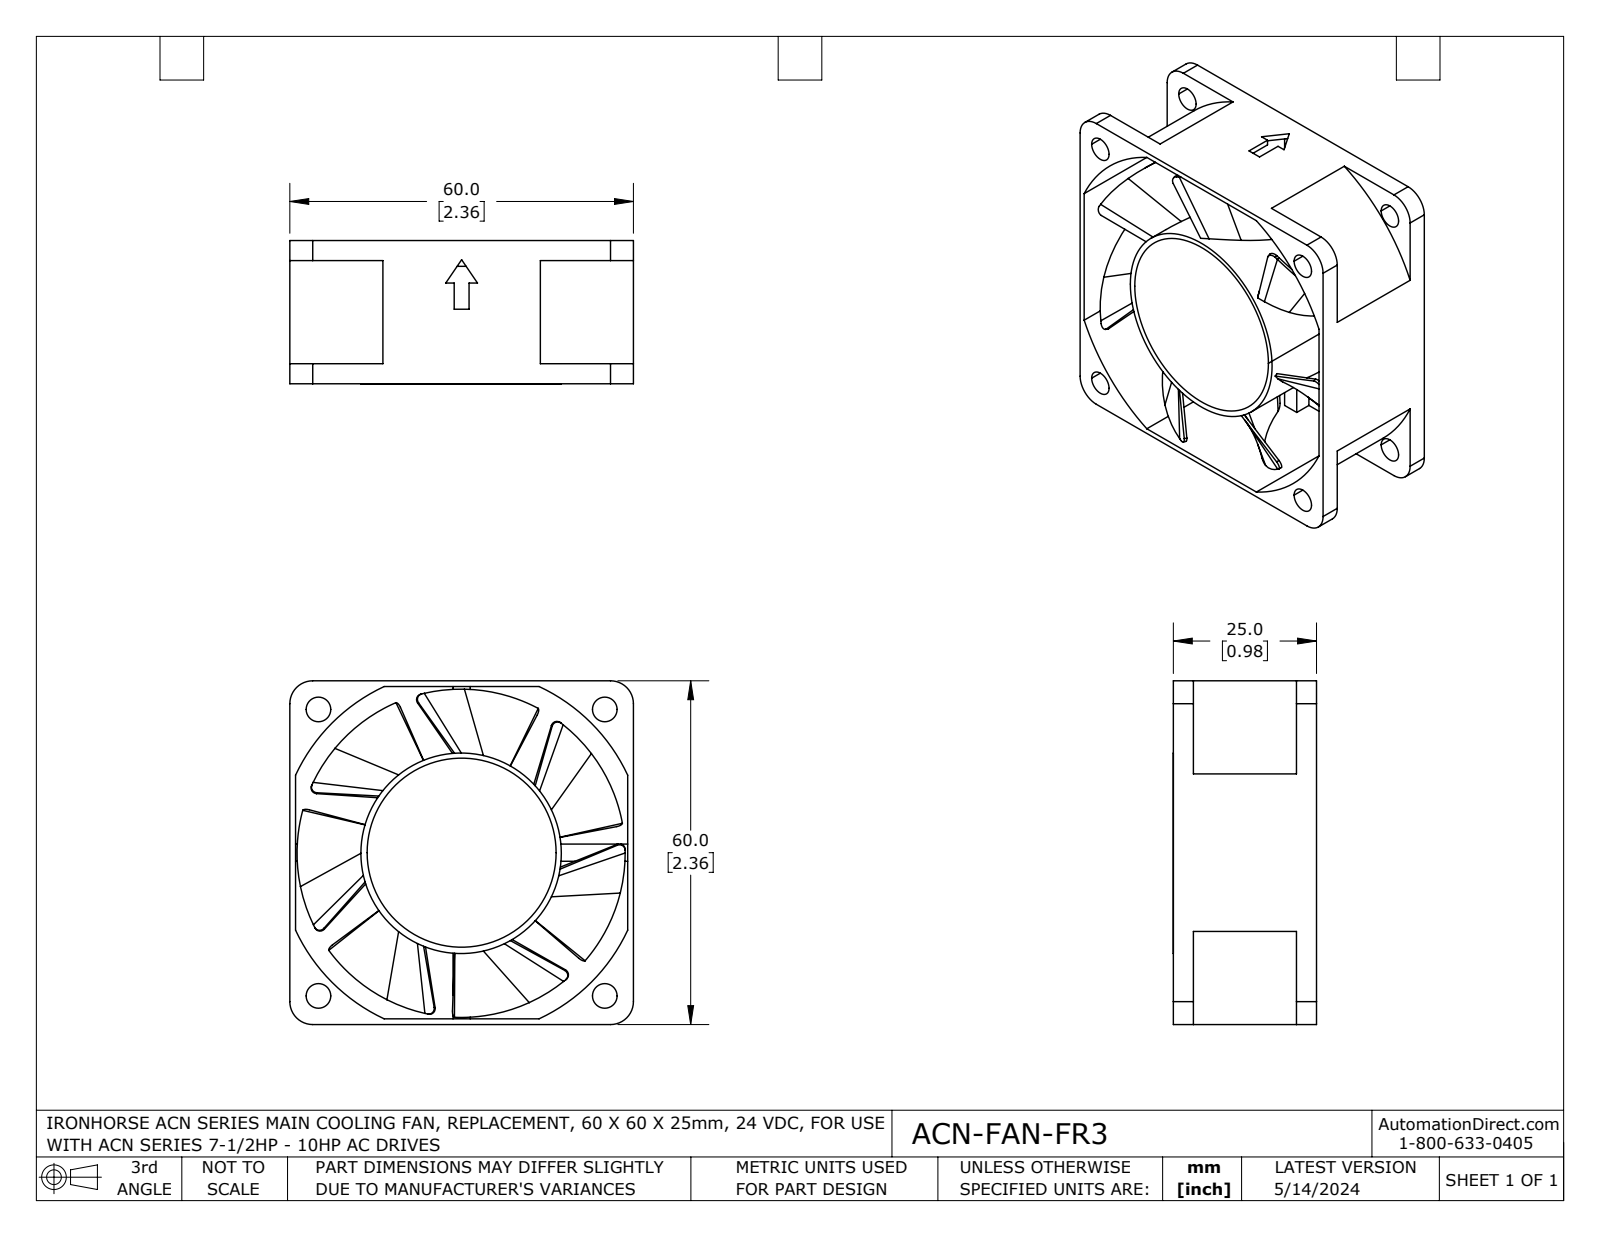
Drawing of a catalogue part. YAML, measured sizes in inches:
part_name: "ACN-FAN-FR3"
step_written_by: "SolidWorks 2021 (AUTOMOTIVE_DESIGN)"
units: inches
bodies: {solids: 2, faces: 187, planar: 42, cylindrical: 40, other: 105}
overall_size: [2.362, 2.362, 0.984]
volume: 2.022
surface_area: 42.74
round_holes:
  - {diameter: 0.169, count: 4}
  - {diameter: 1.161, count: 1}
  - {diameter: 1.299, count: 1}
round_bosses_or_shafts:
  - {diameter: 1.378, count: 1}
  - {diameter: 1.299, count: 1}
partial_cylinders:
  - {radius: 0.157, count: 4}
  - {radius: 1.26, count: 1}
  - {radius: 1.299, count: 1}
face_to_face_distances: [0.039, 2.323, 2.362, 2.283, 0.945, 0.984, 0.941, 0.98, 0.138, 0.846]
hole_center_spacings: [1.392, 1.969, 2.784, 1.386, 1.391, 1.393, 1.398]
